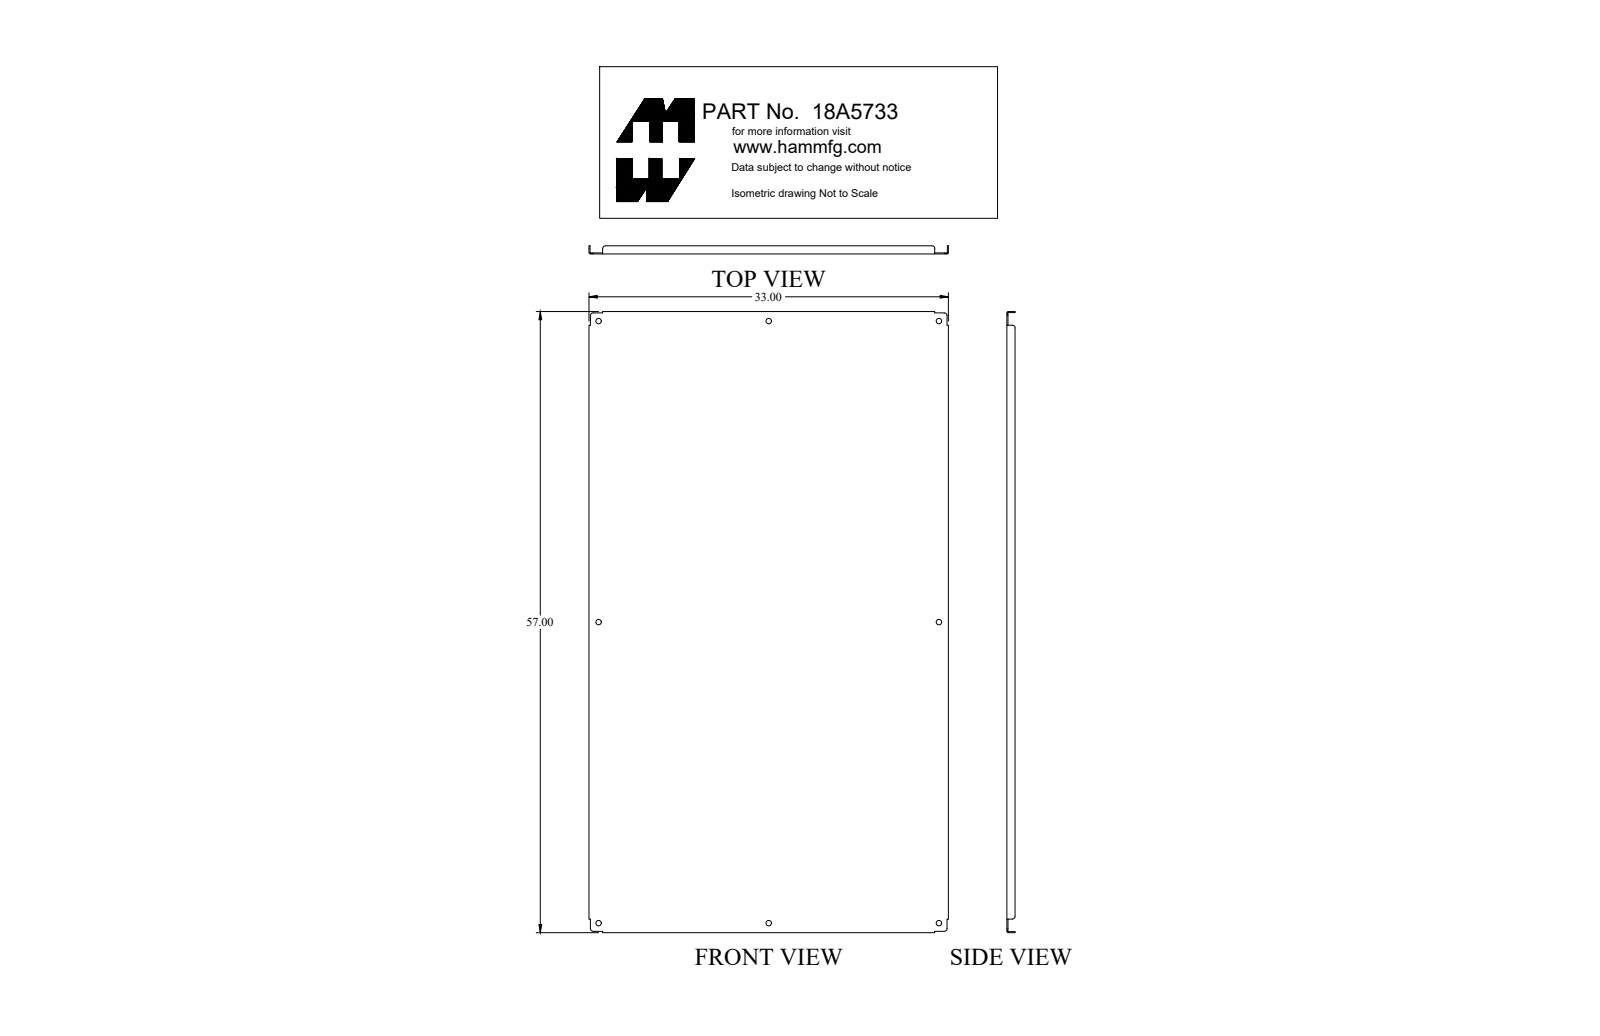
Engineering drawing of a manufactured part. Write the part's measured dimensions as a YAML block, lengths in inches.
part_name: "18A5733"
step_written_by: "SolidWorks 2018 (AUTOMOTIVE_DESIGN)"
units: inches
bodies: {solids: 1, faces: 58, planar: 30, cylindrical: 28, other: 0}
overall_size: [57, 33, 0.75]
volume: 188.5
surface_area: 3986
round_holes:
  - {diameter: 0.5, count: 8}
partial_cylinders:
  - {radius: 0.25, count: 8}
  - {radius: 0.03, count: 4}
  - {radius: 0.125, count: 4}
face_to_face_distances: [0.095, 32.905, 56.905, 33, 32.81, 57, 56.81, 0.75, 0.655, 0.125]
hole_center_spacings: [15.625, 27.625, 31.738, 41.71, 57.417, 31.25, 55.25, 63.475]
